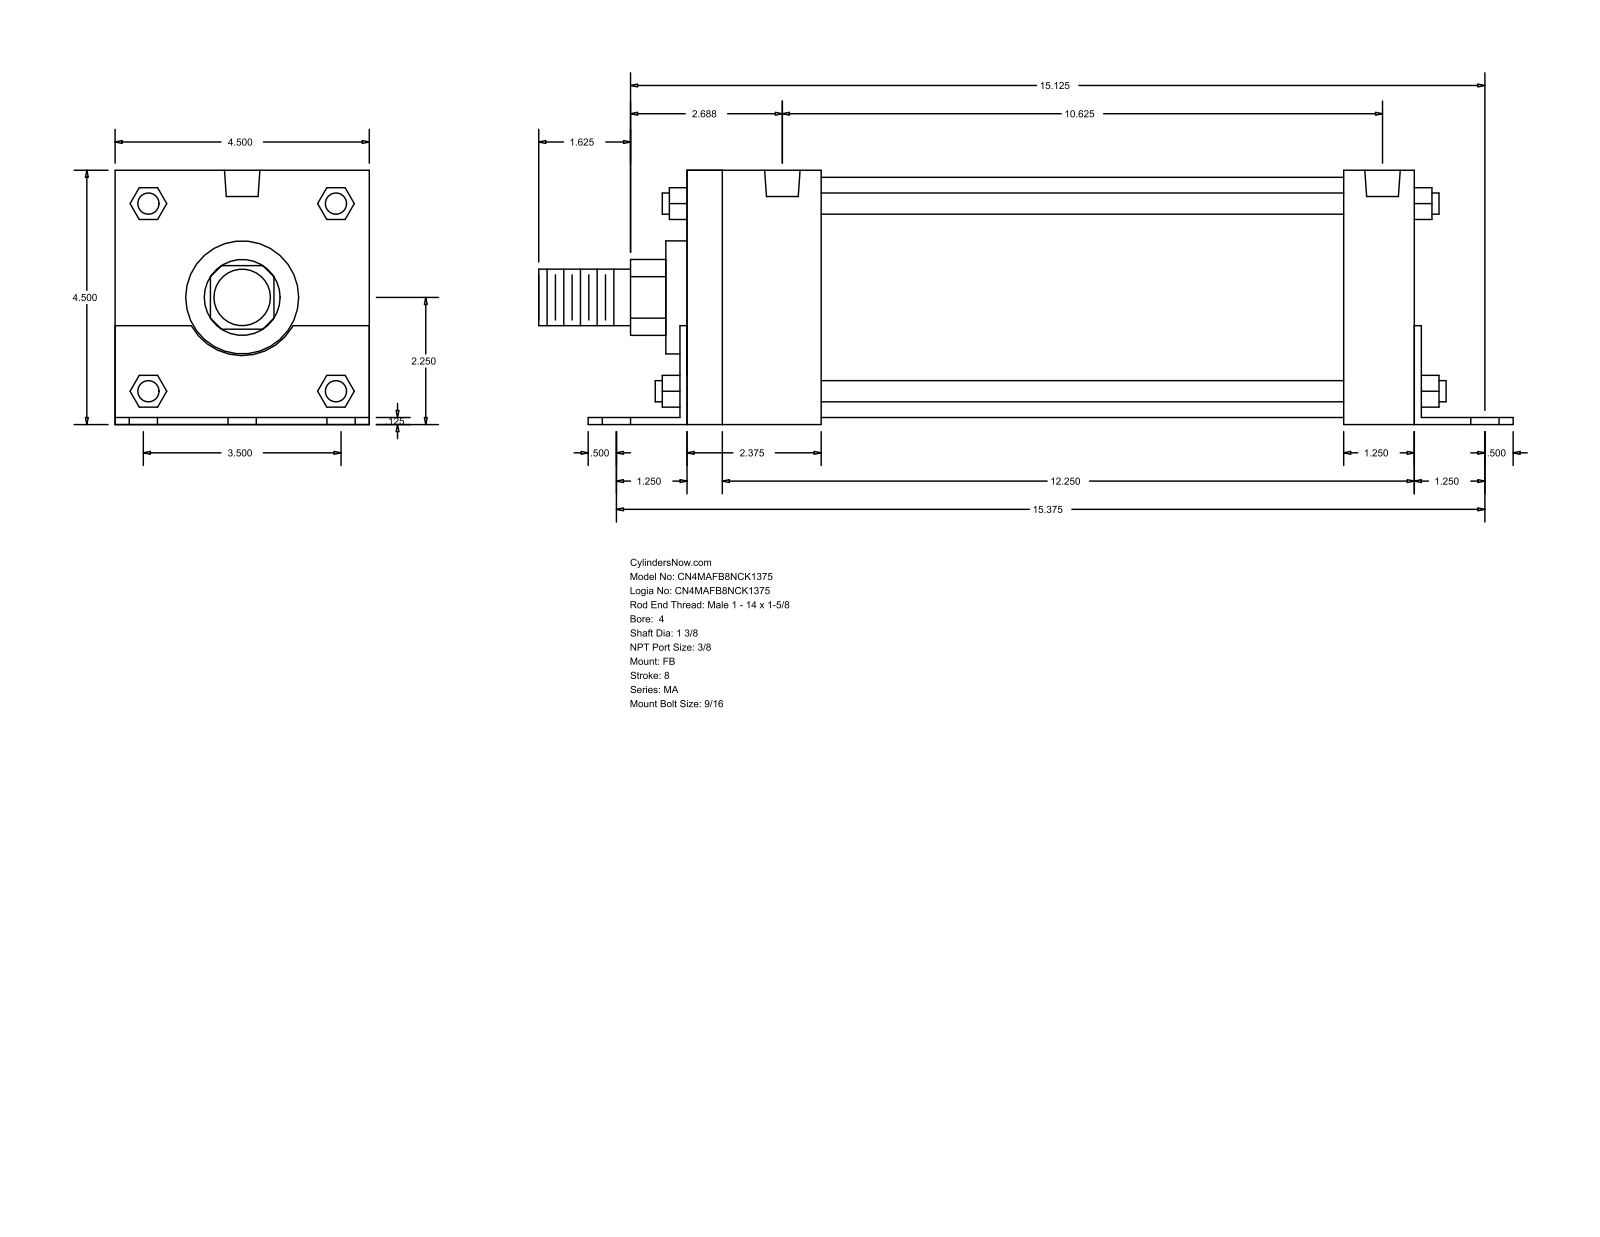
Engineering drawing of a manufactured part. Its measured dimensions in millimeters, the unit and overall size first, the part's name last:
Units: millimetres
Overall size (bounding box): 438.15 × 114.35 × 114.3
Round holes (diameter × count): ⌀14.29 ×6, ⌀11.11 ×4, ⌀15.93 ×2
Round bosses / shafts (diameter × count): ⌀9.53 ×4, ⌀107.95 ×1, ⌀50.8 ×1, ⌀34.92 ×1, ⌀25.4 ×1
Partial cylindrical surfaces — rounded edges, fillets, slot ends (radius × count): R17.06 ×1, R26.16 ×1
Main face-to-face distances: 114.3, 3.17, 114.35, 3.12, 111.18, 330.2, 327.03, 333.37, 31.75, 298.45
Hole centre spacings: 44.45, 393.05, 390.53, 64, 67.5, 86.85, 88.9, 90.98
Bodies: 0 solids, 140 faces (105 planar, 35 cylindrical, 0 other)
Part name (STEP PRODUCT): MA_FB__0400_1.375
STEP written by: GSSL Pune (CONFIG_CONTROL_DESIGN)
